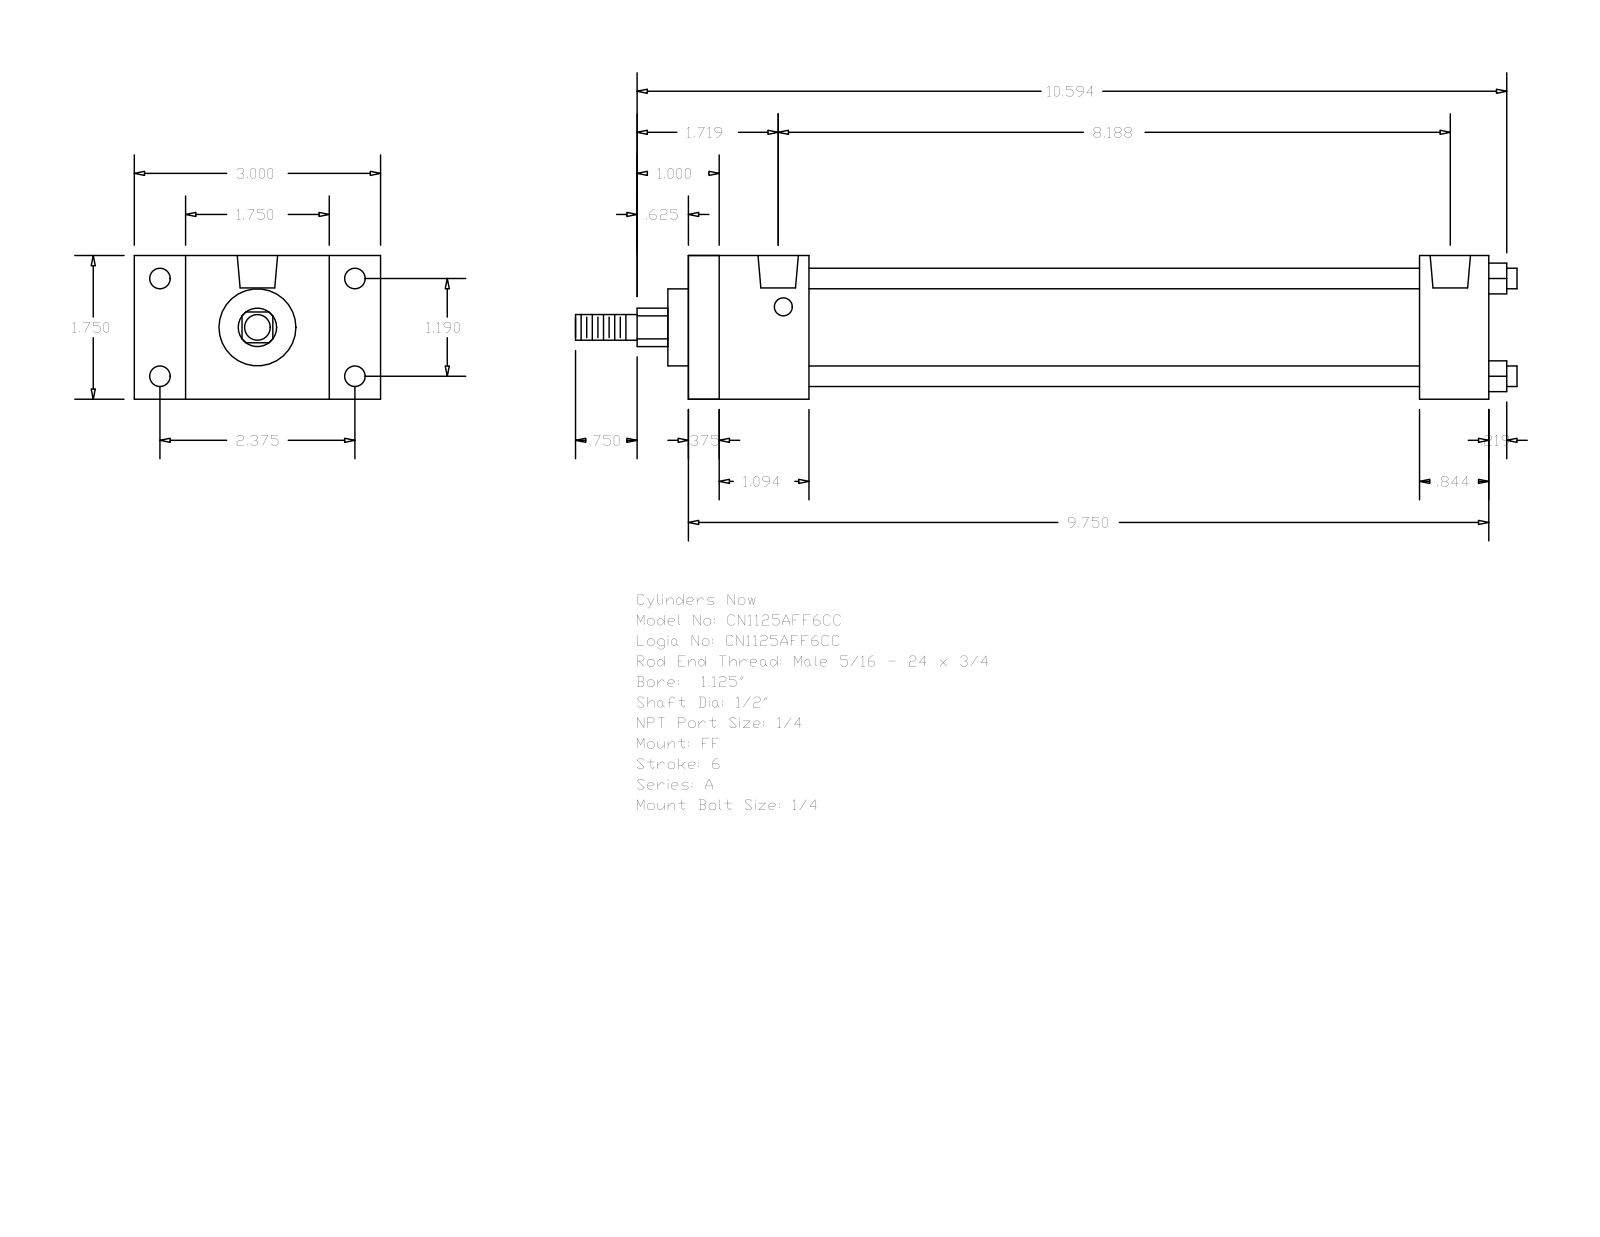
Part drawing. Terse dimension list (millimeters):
name: A_FF__0112_0.5
written by: GSSL Pune (CONFIG_CONTROL_DESIGN)
unit: mm
bodies: 0 solids, 92 faces (64 planar, 28 cylindrical, 0 other)
size: 291.31 × 76.2 × 44.45
holes: 4× ⌀5.56, 4× ⌀6.35, 2× ⌀12.49
bosses: 4× ⌀6.35, 1× ⌀31.88, 1× ⌀23.81, 1× ⌀12.7, 1× ⌀7.94
rounds: 1× R5.94
face distances: 44.46, 247.64, 9.52, 238.12, 15.87, 226.21, 216.69, 21.43, 37.3, 27.78
hole spacings: 30.22, 60.32, 67.47, 204.79, 1.58, 1.59, 206.37, 206.38
